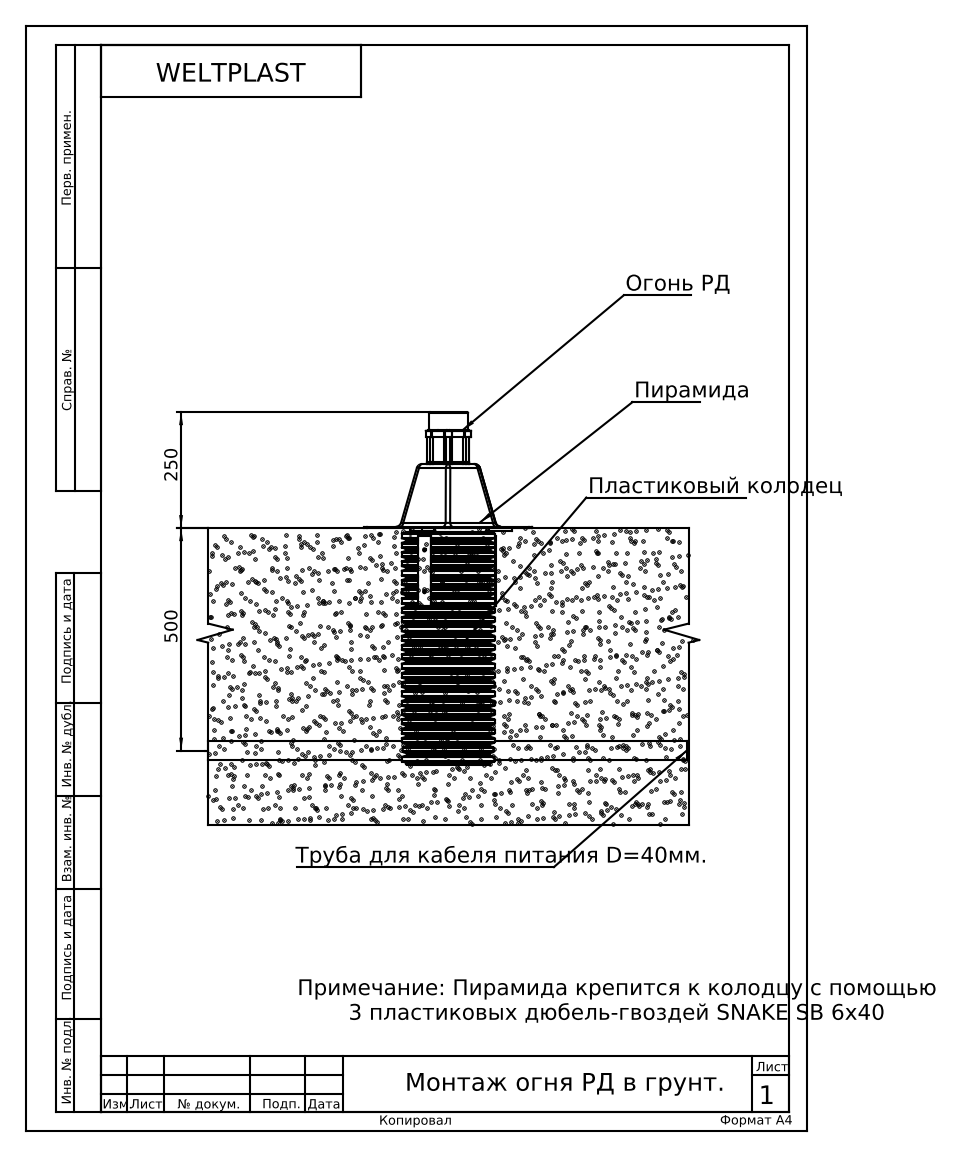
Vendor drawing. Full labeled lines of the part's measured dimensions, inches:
Part name (STEP PRODUCT): LLC-AC-D2; Корпус л.хвост; Сборка фонаря байонет; Конектор мама Сборка 1 (+8 more)
STEP written by: SolidWorks 2018 (AUTOMOTIVE_DESIGN)
Units: inches
Bodies: 41 solids, 1955 faces (626 planar, 805 cylindrical, 524 other)
Overall size (bounding box): 40.496 × 29.852 × 16.219
Volume: 257.8 in³ · Surface area: 2 382 in²
Round holes (diameter × count): ⌀0.173 ×6, ⌀0.177 ×6, ⌀0.236 ×6, ⌀0.256 ×6, ⌀0.197 ×5, ⌀0.209 ×4, ⌀0.157 ×3, ⌀0.165 ×2, ⌀0.496 ×2, ⌀0.797 ×2, ⌀1.024 ×1, ⌀1.575 ×1
Round bosses / shafts (diameter × count): ⌀0.299 ×6, ⌀0.197 ×3, ⌀0.157 ×3, ⌀0.846 ×2, ⌀0.776 ×2, ⌀0.591 ×2, ⌀7.874 ×1, ⌀7.087 ×1
Partial cylindrical surfaces — rounded edges, fillets, slot ends (radius × count): R0.079 ×28, R0.472 ×26, R0.197 ×25, R0.177 ×18, R0.039 ×16, R0.059 ×14, R0.118 ×12, R0.276 ×9
Main face-to-face distances: 0.118, 0.059, 0.236, 0.079, 2.539, 0.512, 0.827, 0.591, 0.748, 5.315
Hole centre spacings: 1.87, 3.239, 1.621, 1.893, 2.198, 1.665, 3.543, 3.74
